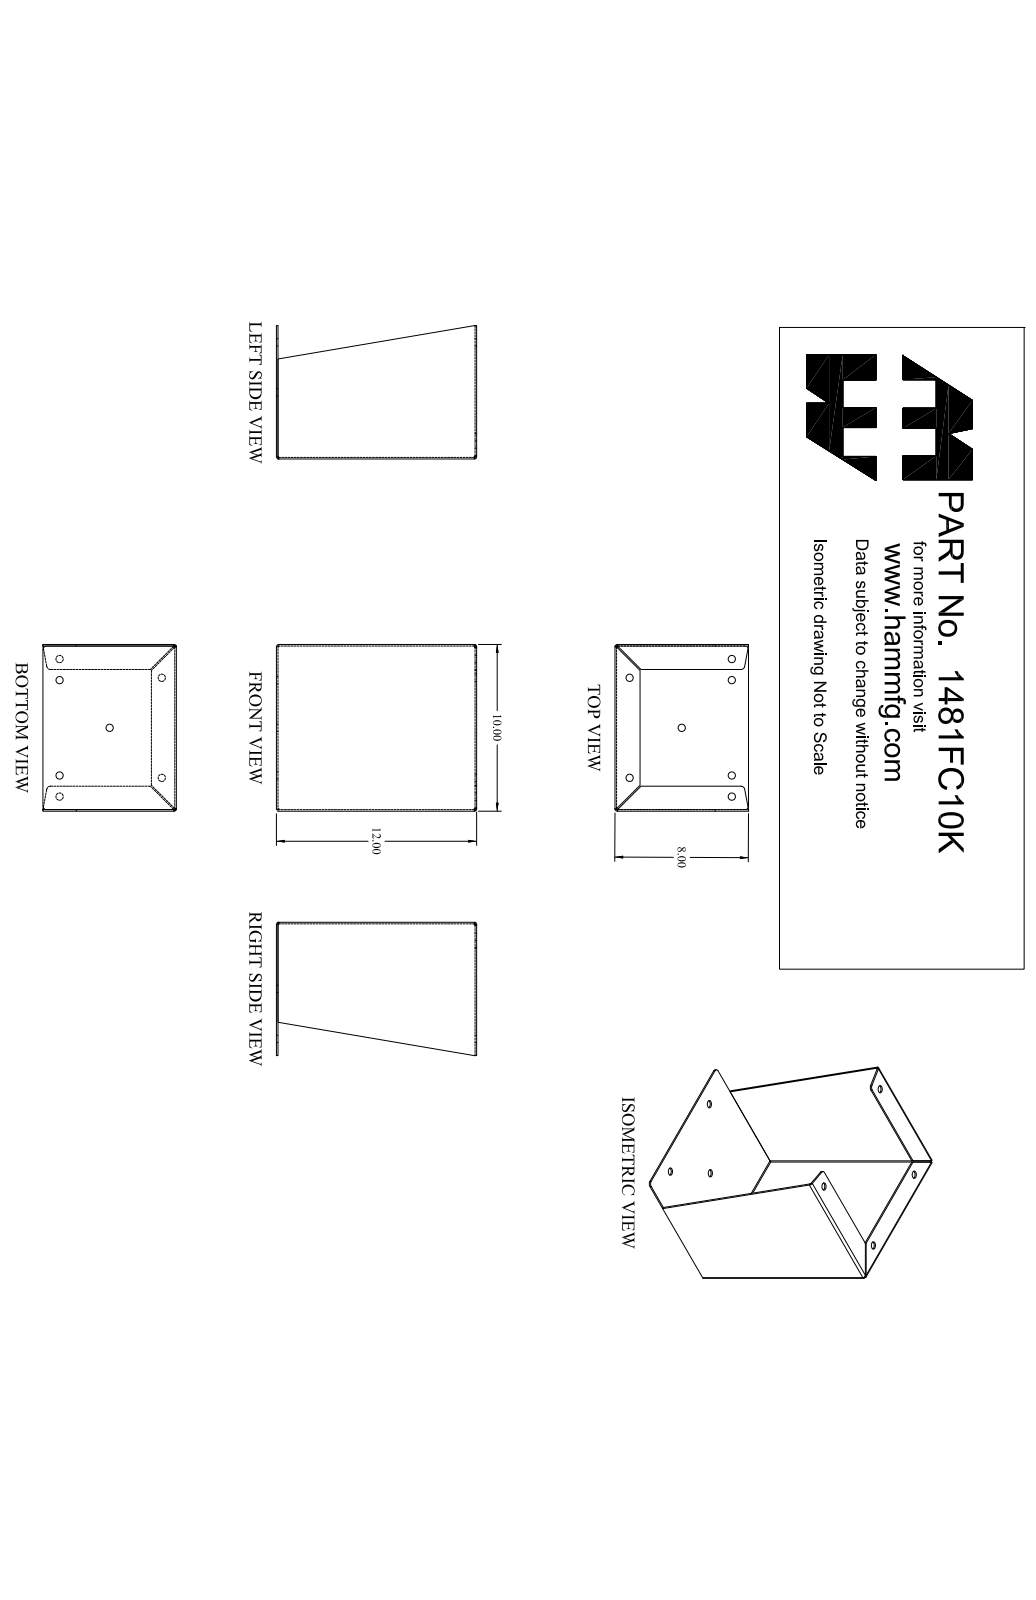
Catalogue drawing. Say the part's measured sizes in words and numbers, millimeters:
The part is named "1481FC10K_Default". Its 3-D file was written by "SolidWorks 2019 (CONFIG_CONTROL_DESIGN)". It is 1 solid with 78 faces: 42 planar, 30 cylindrical and 6 other. Overall it measures 304.8 by 254 by 203.2 millimeters. Its volume is 607 100 cubic millimeters and its surface area 509 500 square millimeters. Round holes: 7 of diameter 11.1. Partial cylindrical surfaces (rounded edges, fillets, slot ends): 6 of radius 1.2, 6 of radius 3.6, 4 of radius 5.6. The main face-to-face distances are 2.4, 251.6, 249.2, 254, 2.4, 300, 302.4, 302.4, 304.8, 35.7. The hole center spacings are 32.2, 105.3, 110, 129.6, 155.6, 158.2, 177.4, 215.3.
